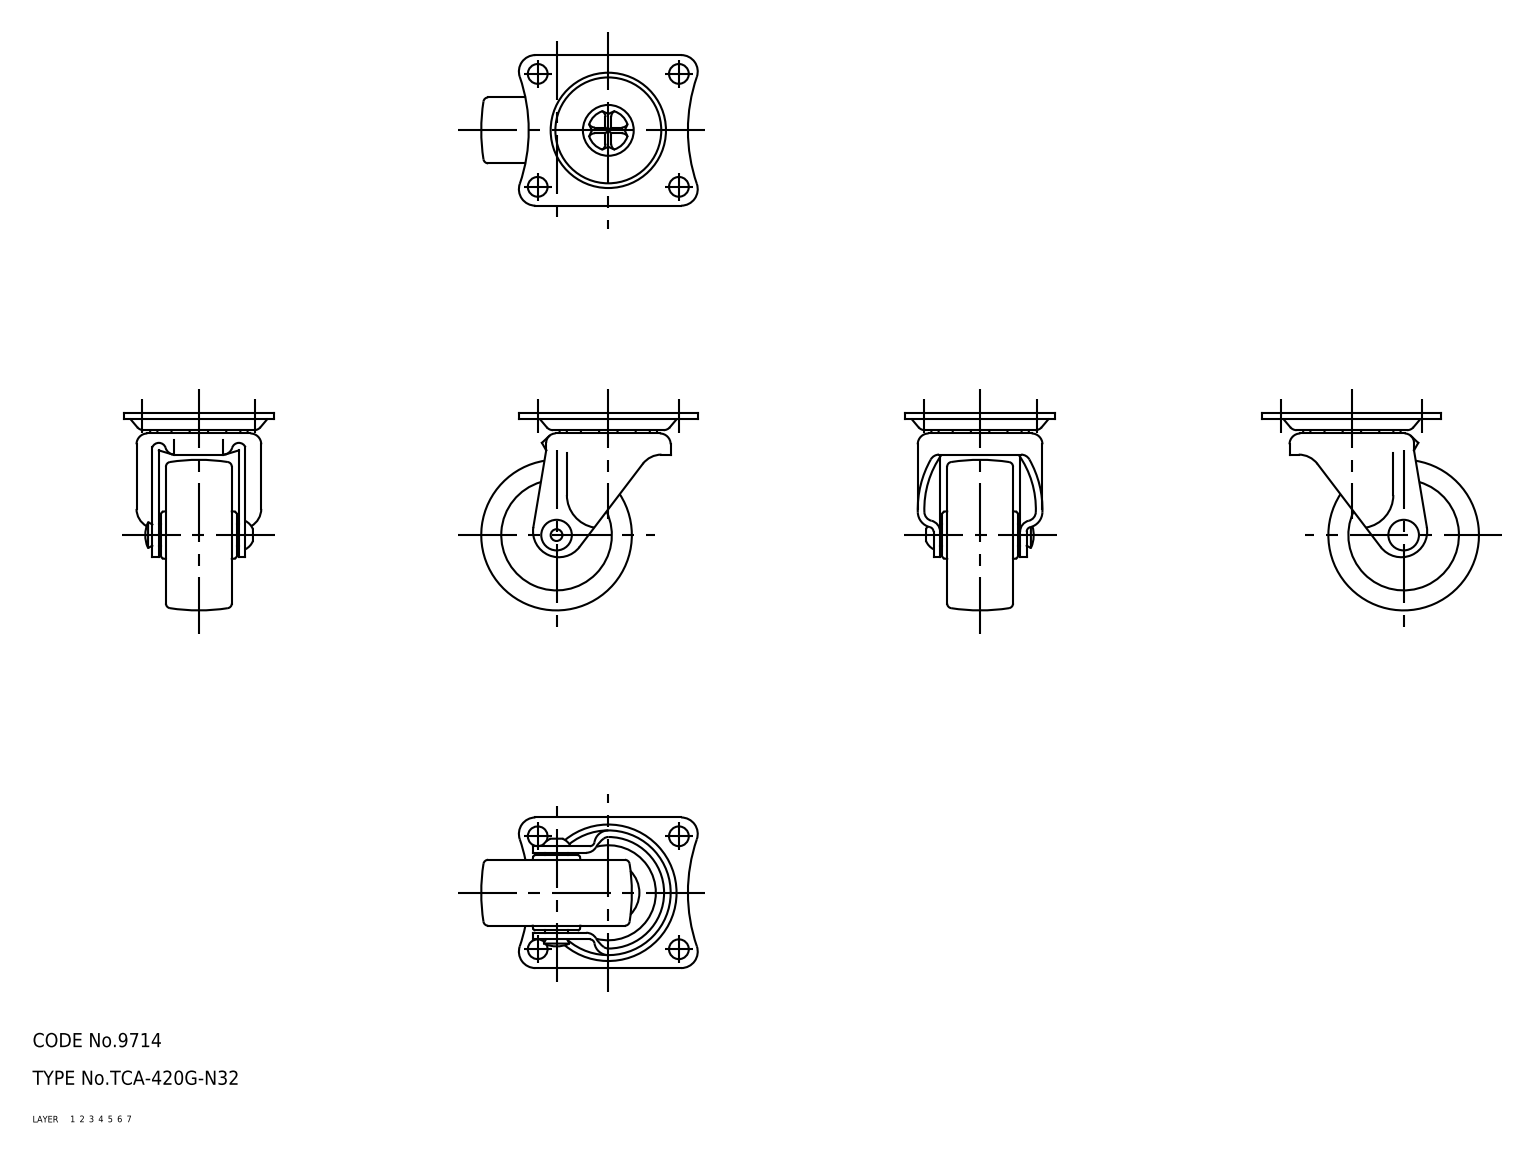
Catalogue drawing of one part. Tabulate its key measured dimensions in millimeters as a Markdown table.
| quantity | value |
| --- | --- |
| part name | wheel; mounting plate; main shaft; axle (+1 more) |
| STEP written by | CADfix (AUTOMOTIVE_DESIGN) |
| units | millimeters |
| bodies | 5 solids, 247 faces (0 planar, 0 cylindrical, 247 other) |
| overall size | 46 × 42 × 32 |
| volume | 13 809 mm³ |
| surface area | 10 576 mm² |
